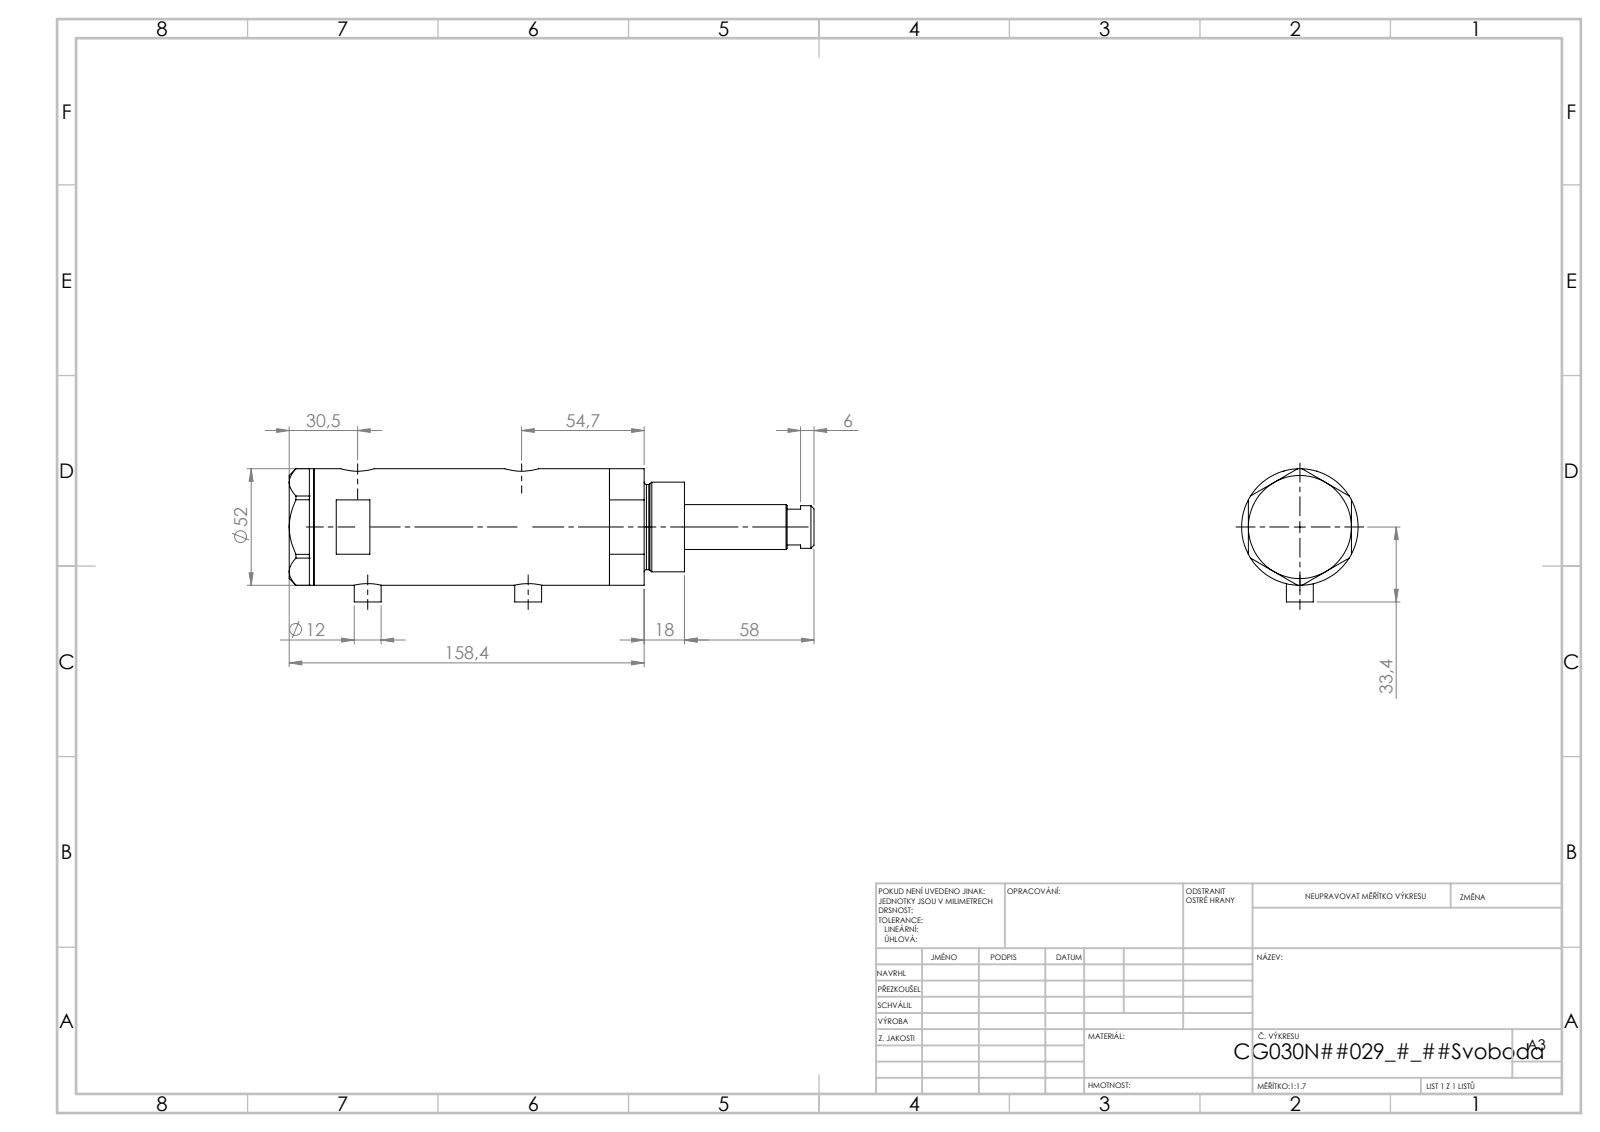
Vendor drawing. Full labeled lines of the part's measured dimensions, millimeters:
Part name (STEP PRODUCT): V270CG_MIDDLE; V270CG_VC; V270CG_BACK; V270CG_FRONT
STEP written by: SolidWorks 2019 (CONFIG_CONTROL_DESIGN)
Units: millimetres
Bodies: 4 solids, 140 faces (67 planar, 53 cylindrical, 20 other)
Overall size (bounding box): 234.2 × 59.4 × 52
Volume: 352 471 mm³ · Surface area: 81 437 mm²
Round holes (diameter × count): ⌀5 ×2, ⌀9.73 ×2, ⌀12.5 ×2, ⌀15 ×2, ⌀6.5 ×1, ⌀20 ×1, ⌀21.5 ×1, ⌀30 ×1, ⌀33 ×1, ⌀44 ×1
Round bosses / shafts (diameter × count): ⌀12 ×2, ⌀52 ×1, ⌀40 ×1, ⌀38 ×1, ⌀19 ×1
Main face-to-face distances: 95.5, 23.8, 71.7, 11, 34.8, 106.5, 46, 142.9, 131.9, 108.1
Hole centre spacings: 2.9, 4.5, 68.7, 71.6, 73.2, 76.1
